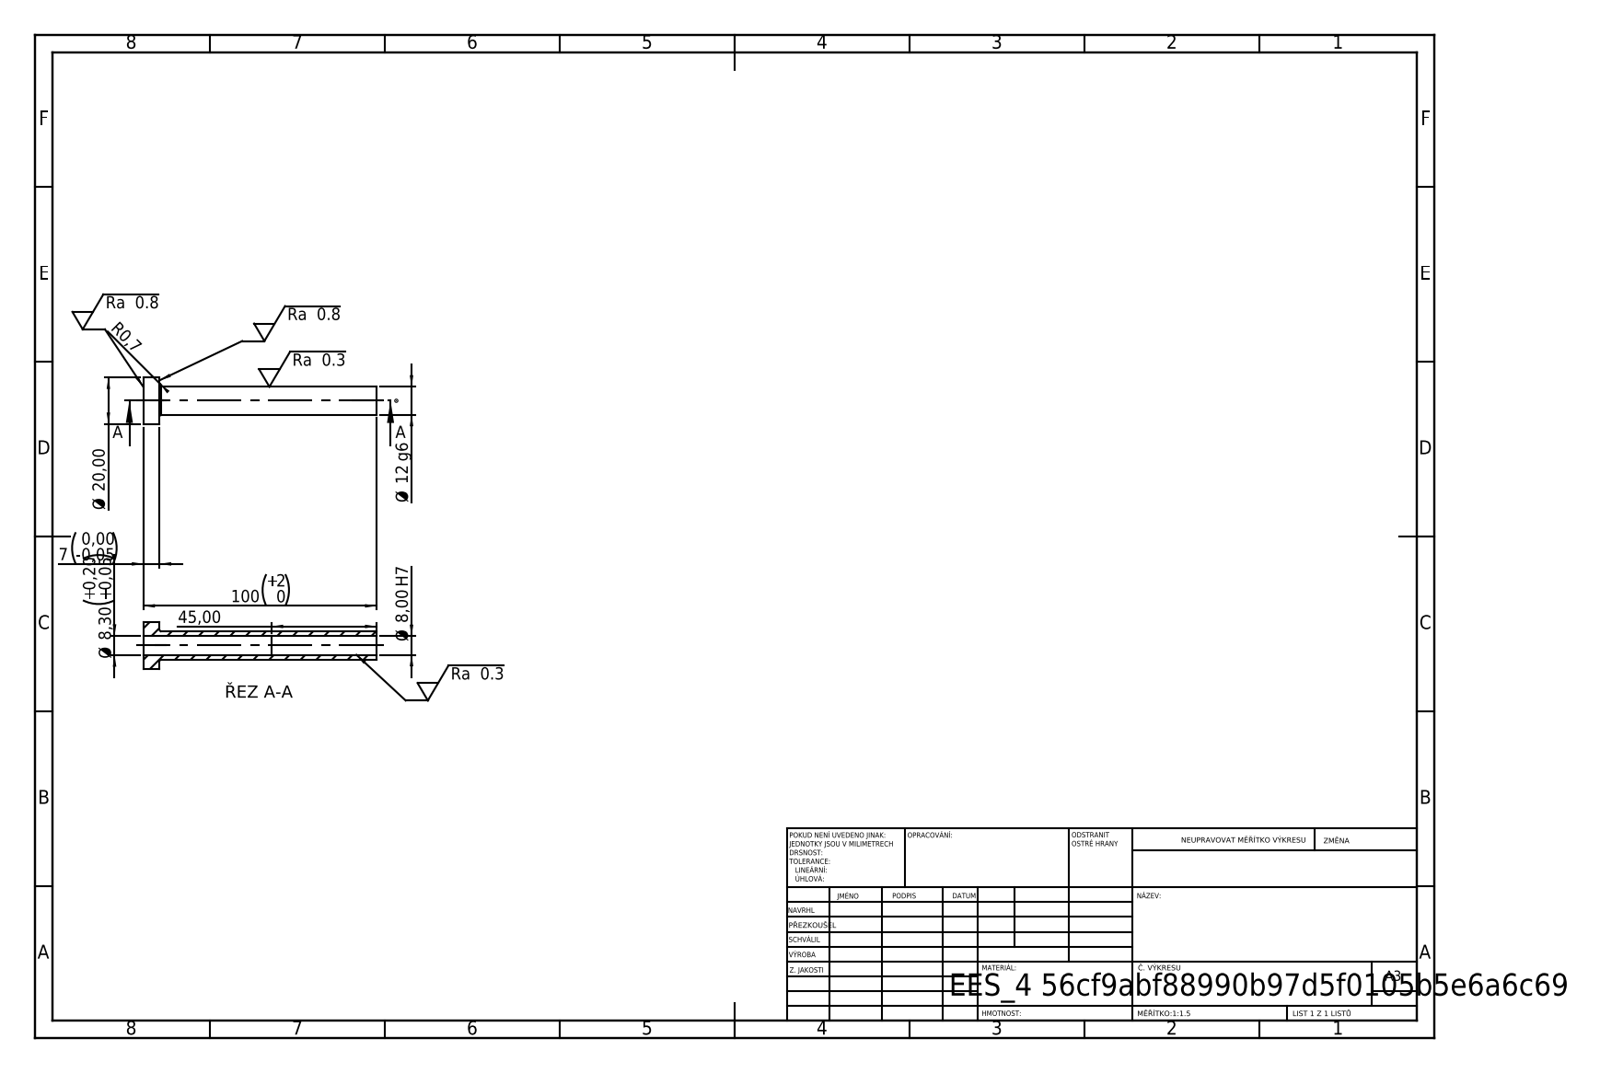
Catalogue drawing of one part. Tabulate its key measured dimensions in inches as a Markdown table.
| quantity | value |
| --- | --- |
| STEP written by | SolidWorks 2019 (CONFIG_CONTROL_DESIGN) |
| units | inches |
| bodies | 1 solid, 14 faces (4 planar, 8 cylindrical, 2 other) |
| overall size | 3.937 × 0.787 × 0.787 |
| volume | 0.457 in³ |
| surface area | 10.89 in² |
| round holes (diameter × count) | 0.315 × 1, 0.327 × 1 |
| round bosses / shafts (diameter × count) | 0.787 × 1, 0.472 × 1 |
| main face-to-face distances | 0.276, 3.937, 3.661, 2.165, 1.89, 1.772 |
